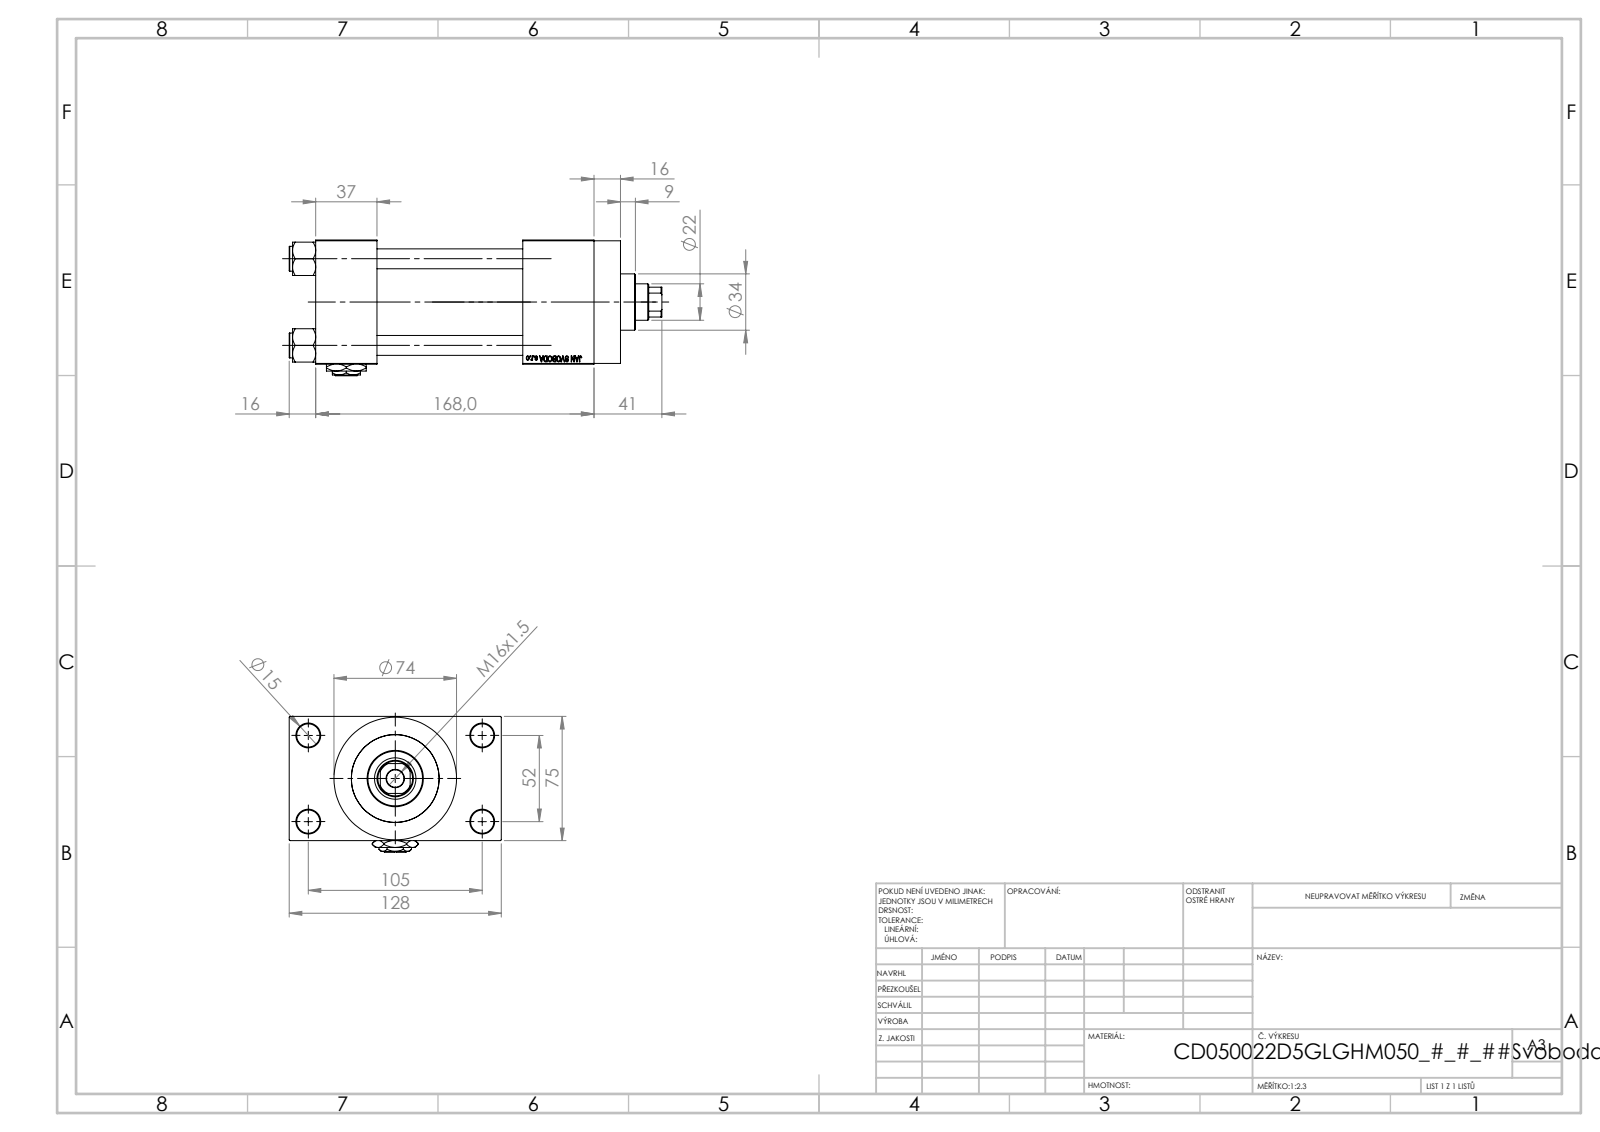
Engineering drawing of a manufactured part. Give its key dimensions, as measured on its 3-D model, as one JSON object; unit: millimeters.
{"part_name": "V215CD_D_Body; Zatka_pro_OIL_PORT; V215CD_NUT_M5_D; V215CD_VCP_D (+2 more)", "step_written_by": "SolidWorks 2019 (CONFIG_CONTROL_DESIGN)", "units": "millimeters", "bodies": {"solids": 12, "faces": 1146, "planar": 519, "cylindrical": 89, "other": 538}, "overall_size": [225, 128, 82], "volume_mm3": 849267, "surface_area_mm2": 182994, "round_holes": [[12, 4], [14, 4], [7, 2], [20.96, 2], [30, 2], [10.5, 1], [22, 1], [25, 1], [41, 1], [50, 1], [53, 1]], "round_bosses_or_shafts": [[15, 4], [74, 1], [56, 1], [34, 1]], "partial_cylinders_radius": [[10.5, 1]], "face_to_face_distances": [75, 88, 37, 125, 26.5, 101.5, 43, 168, 131, 16], "hole_center_spacings": [26.35, 36.98, 52.3, 58.43, 58.59, 78.65, 94.37, 52]}
